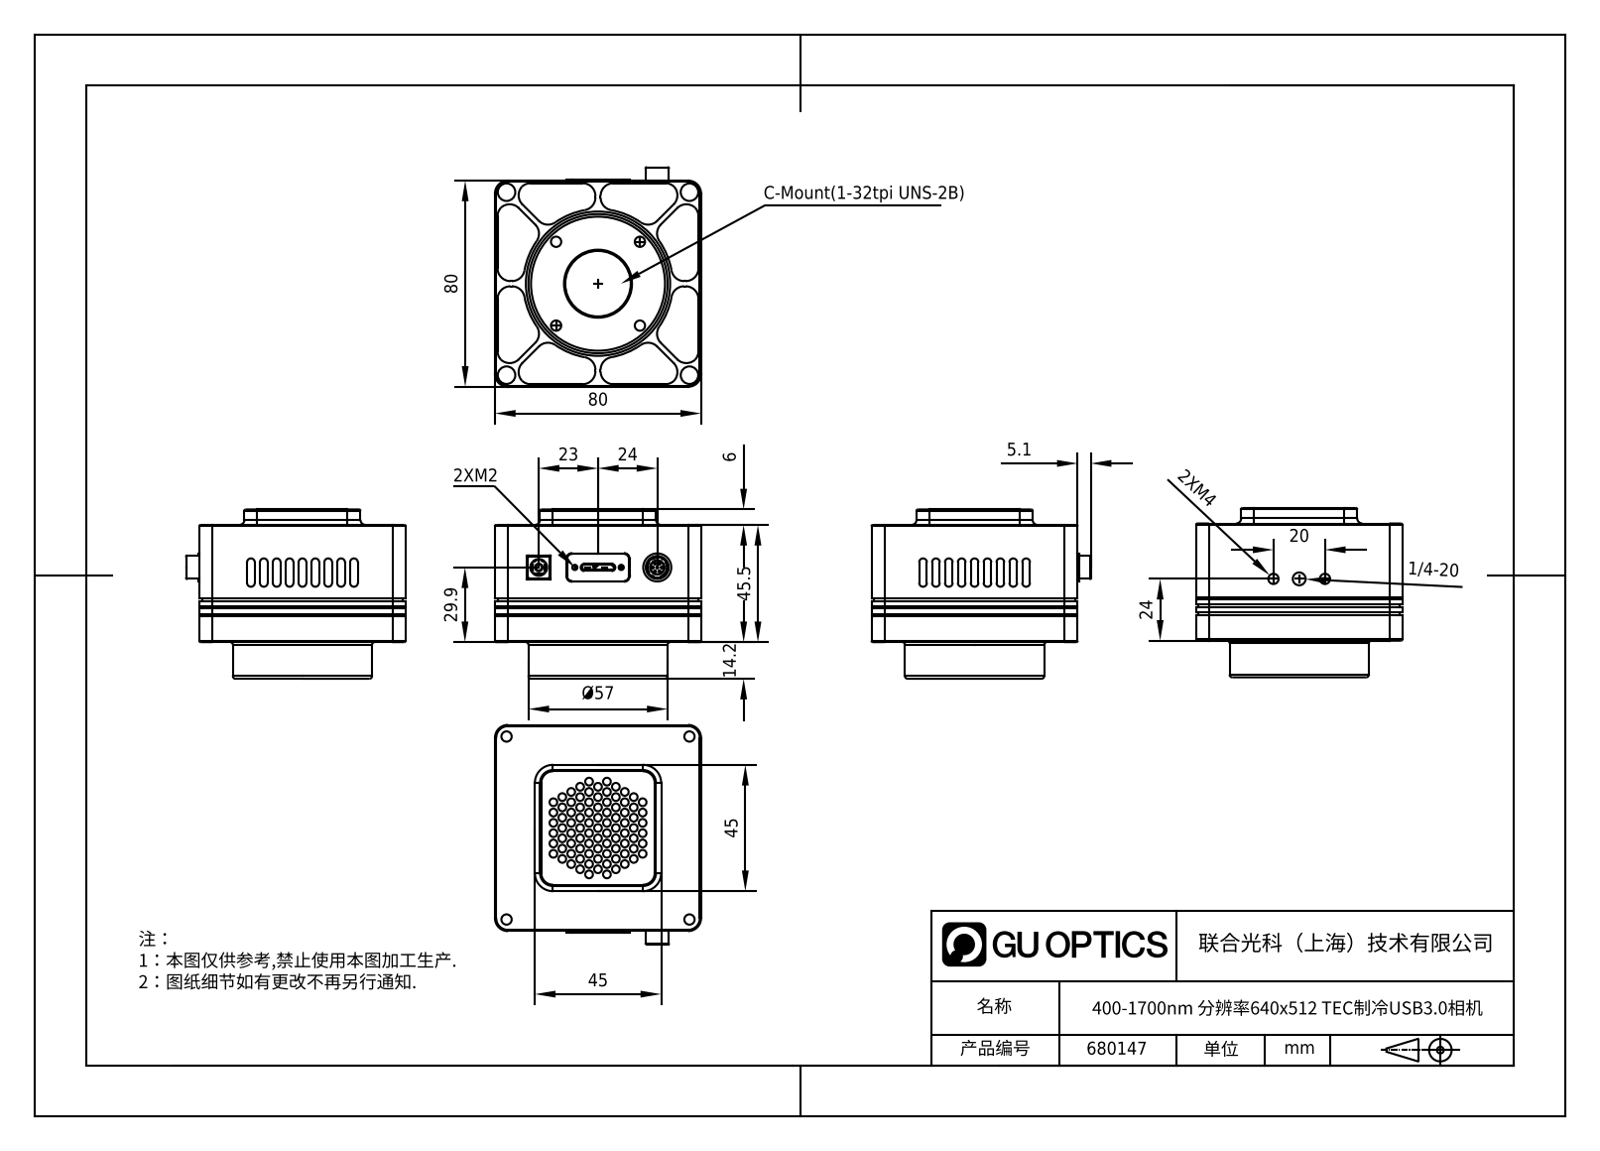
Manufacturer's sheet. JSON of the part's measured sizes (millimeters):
{"part_name": "680136", "step_written_by": "SolidWorks 2020 (CONFIG_CONTROL_DESIGN)", "units": "millimeters", "bodies": {"solids": 16, "faces": 1748, "planar": 907, "cylindrical": 715, "other": 126}, "overall_size": [85.1, 80, 65.7], "volume_mm3": 314598, "surface_area_mm2": 44584, "round_holes": [[3, 89], [4, 10], [0.8, 7], [6.8, 4], [1.6, 2], [2.85, 1], [5, 1], [5.8, 1], [25.4, 1]], "round_bosses_or_shafts": [[1.2, 9], [0.5, 7], [3.6, 2], [54, 1], [10.9, 1], [8.9, 1], [7.9, 1], [5.6, 1]], "partial_cylinders_radius": [[5, 48], [0.2, 47], [0.5, 41], [0.15, 39], [1.5, 18], [2, 16], [0.25, 12], [0.1, 6]], "face_to_face_distances": [80, 1, 42.5, 3, 6, 17.2, 10, 5, 59.7, 11], "hole_center_spacings": [6.93, 10.58, 4, 8, 4.01, 18.33, 12, 55.22]}
